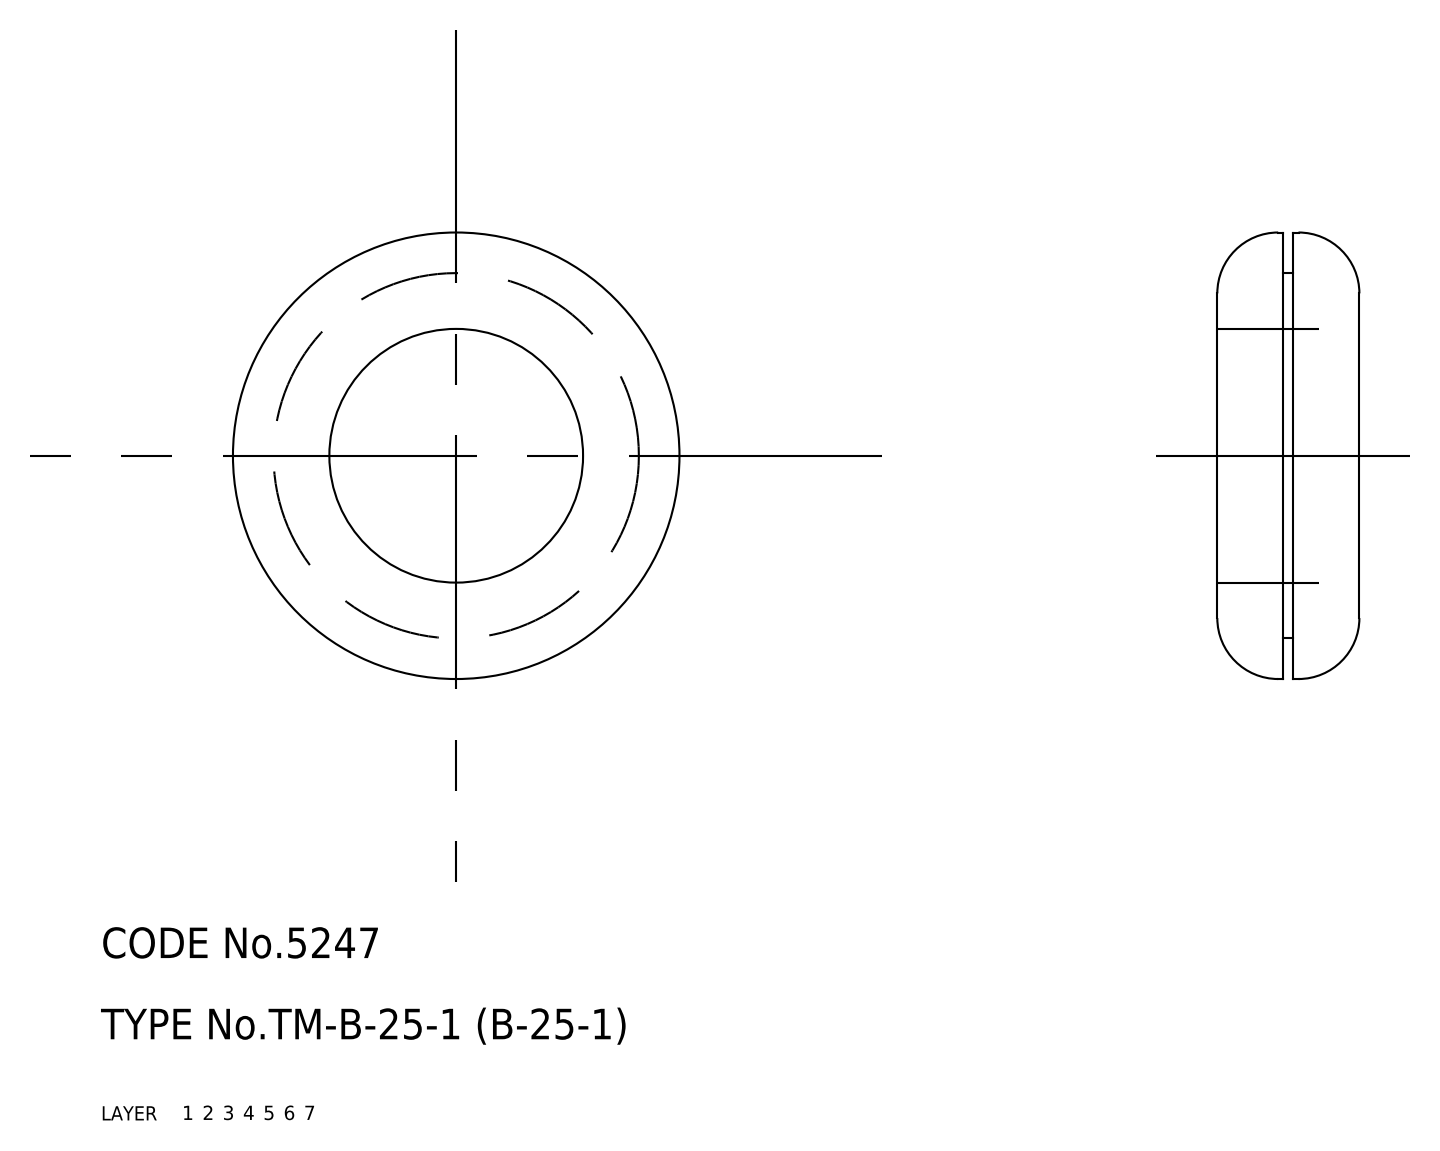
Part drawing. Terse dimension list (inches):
name: grommet
written by: CADfix (AUTOMOTIVE_DESIGN)
unit: in
bodies: 1 solid, 16 faces (0 planar, 0 cylindrical, 16 other)
size: 1.732 × 1.732 × 0.551
volume: 0.729 in³; area: 8.266 in²
